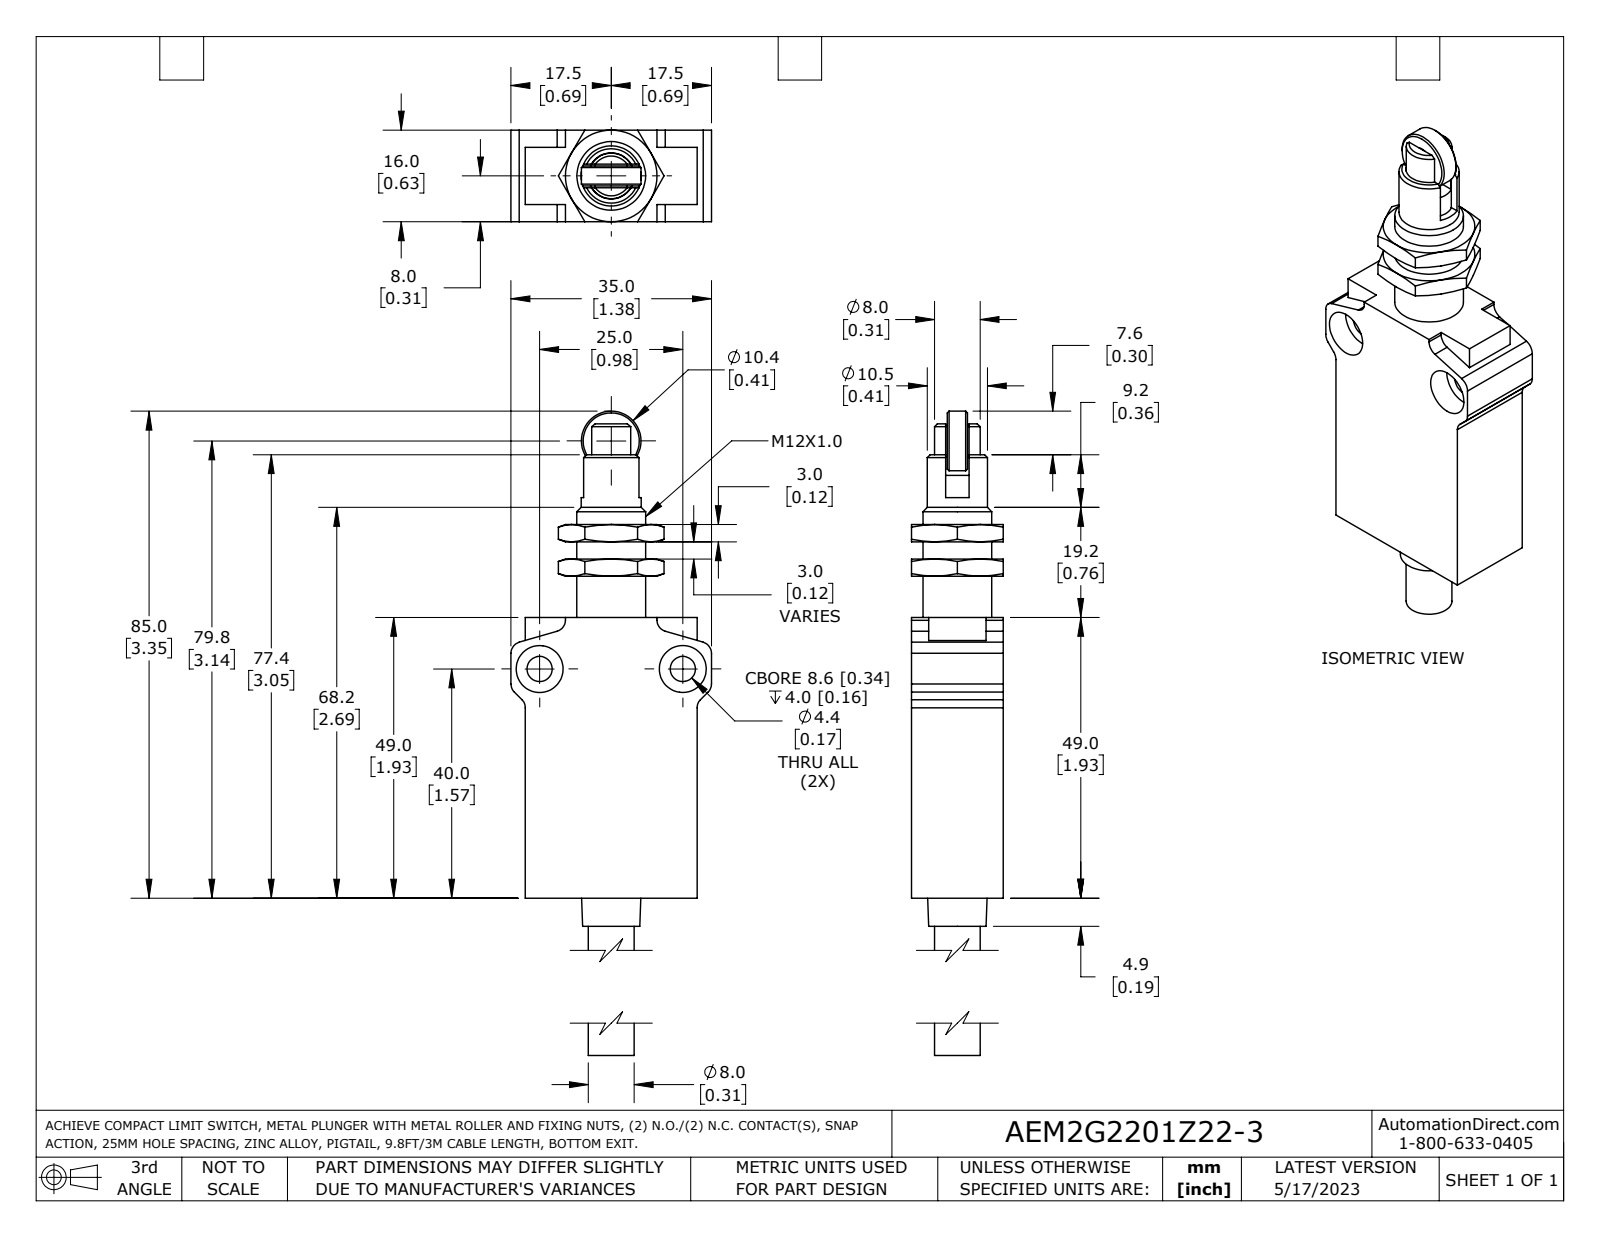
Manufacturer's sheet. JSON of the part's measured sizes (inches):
{"part_name": "AEM2G2201Z22-3", "step_written_by": "SolidWorks 2021 (AUTOMOTIVE_DESIGN)", "units": "inches", "bodies": {"solids": 3, "faces": 141, "planar": 74, "cylindrical": 31, "other": 36}, "overall_size": [3.933, 1.378, 0.63], "volume_in3": 1.668, "surface_area_in2": 16.14, "round_holes": [[0.173, 2], [0.323, 2], [0.317, 1], [0.472, 1]], "round_bosses_or_shafts": [[0.413, 1], [0.409, 1], [0.315, 1], [0.313, 1], [0.22, 1]], "partial_cylinders_radius": [[0.079, 8], [0.256, 1]], "face_to_face_distances": [0.63, 1.181, 0.118, 1.929, 0.236, 0.354, 0.472, 0.098, 1.28, 0.15], "hole_center_spacings": [0.984]}
